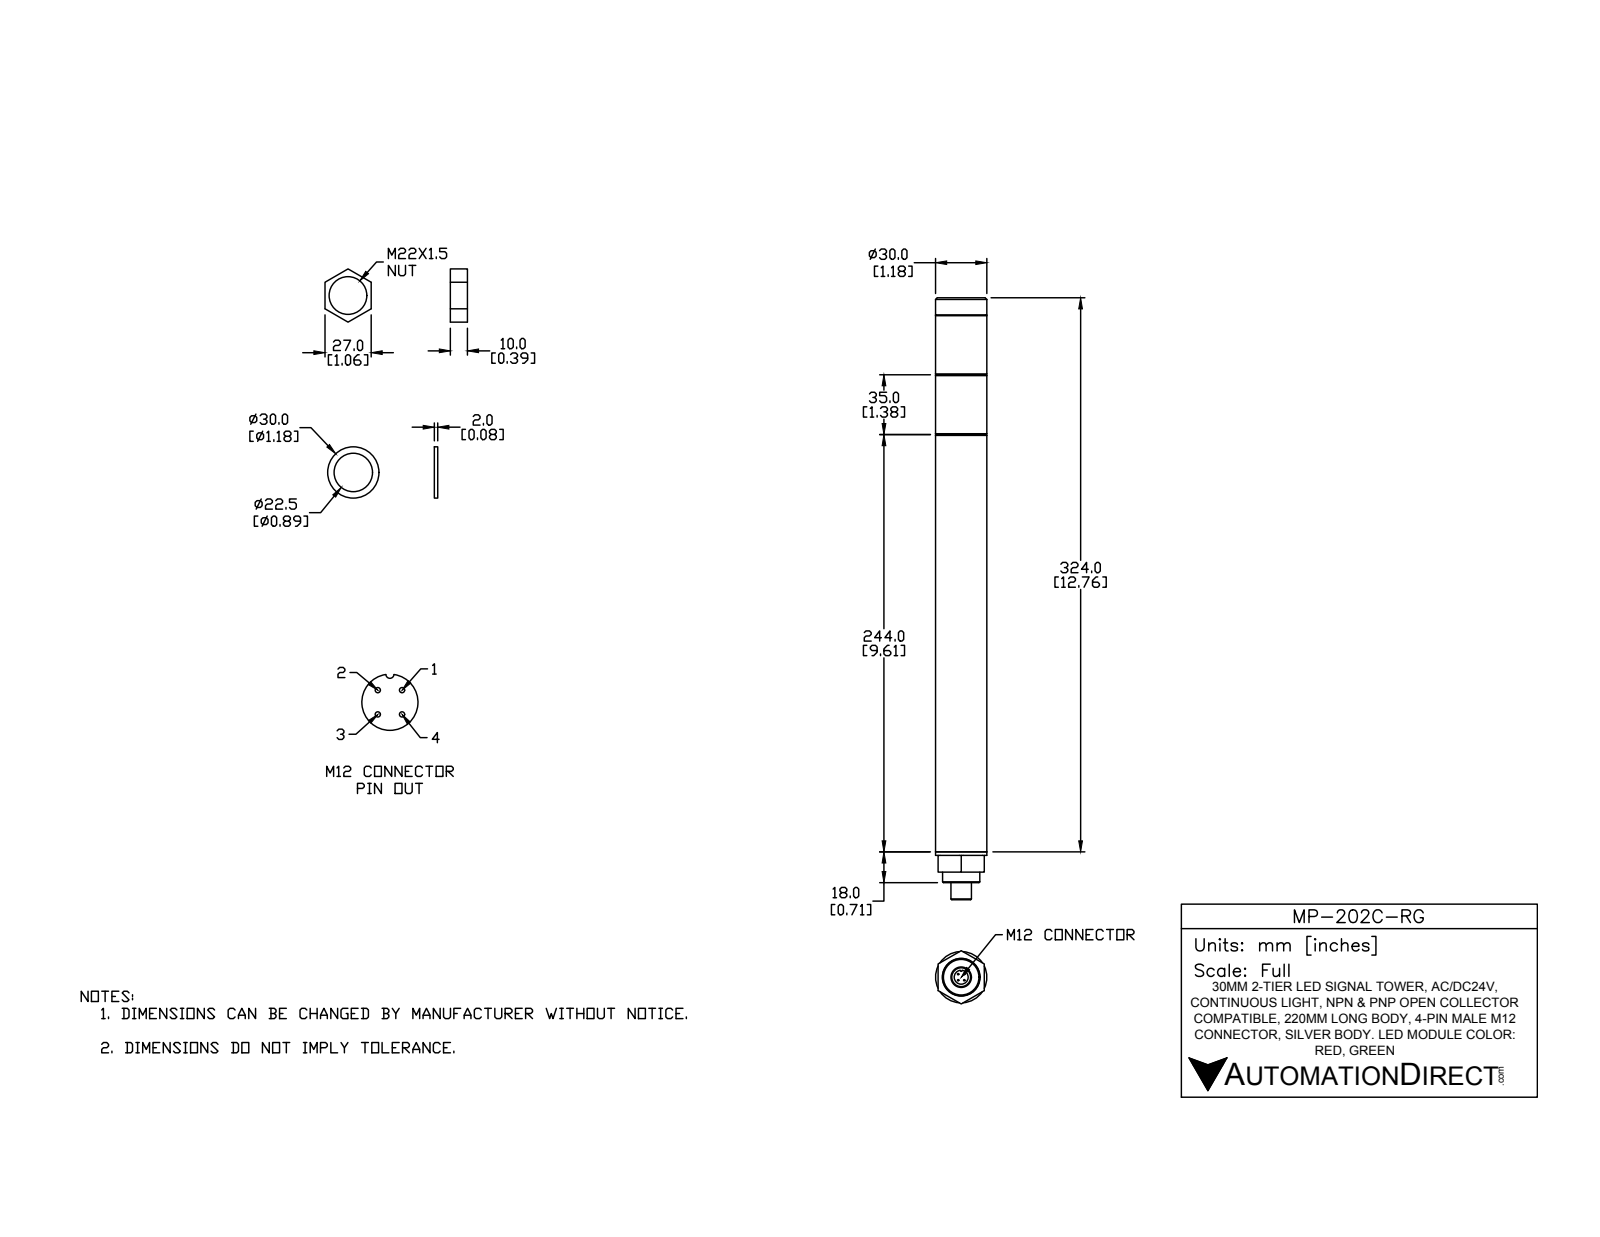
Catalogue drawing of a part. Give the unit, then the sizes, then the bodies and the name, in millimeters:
Units: millimetres
Overall size (bounding box): 352 × 31.18 × 30
Round holes (diameter × count): ⌀3.2 ×1, ⌀7.7 ×1, ⌀8.2 ×1, ⌀20.7 ×1, ⌀22 ×1
Round bosses / shafts (diameter × count): ⌀0.75 ×4, ⌀30 ×1, ⌀21.8 ×1, ⌀12 ×1, ⌀5 ×1
Partial cylindrical surfaces — rounded edges, fillets, slot ends (radius × count): R0.6 ×1
Main face-to-face distances: 35, 70, 244, 279, 314, 246, 281, 10, 2, 316
Volume: 228 168 mm³ · Surface area: 43 994 mm²
Bodies: 11 solids, 106 faces (43 planar, 37 cylindrical, 26 other)
Part name (STEP PRODUCT): MP-202C-RG
STEP written by: SolidWorks 2016 (AUTOMOTIVE_DESIGN)
